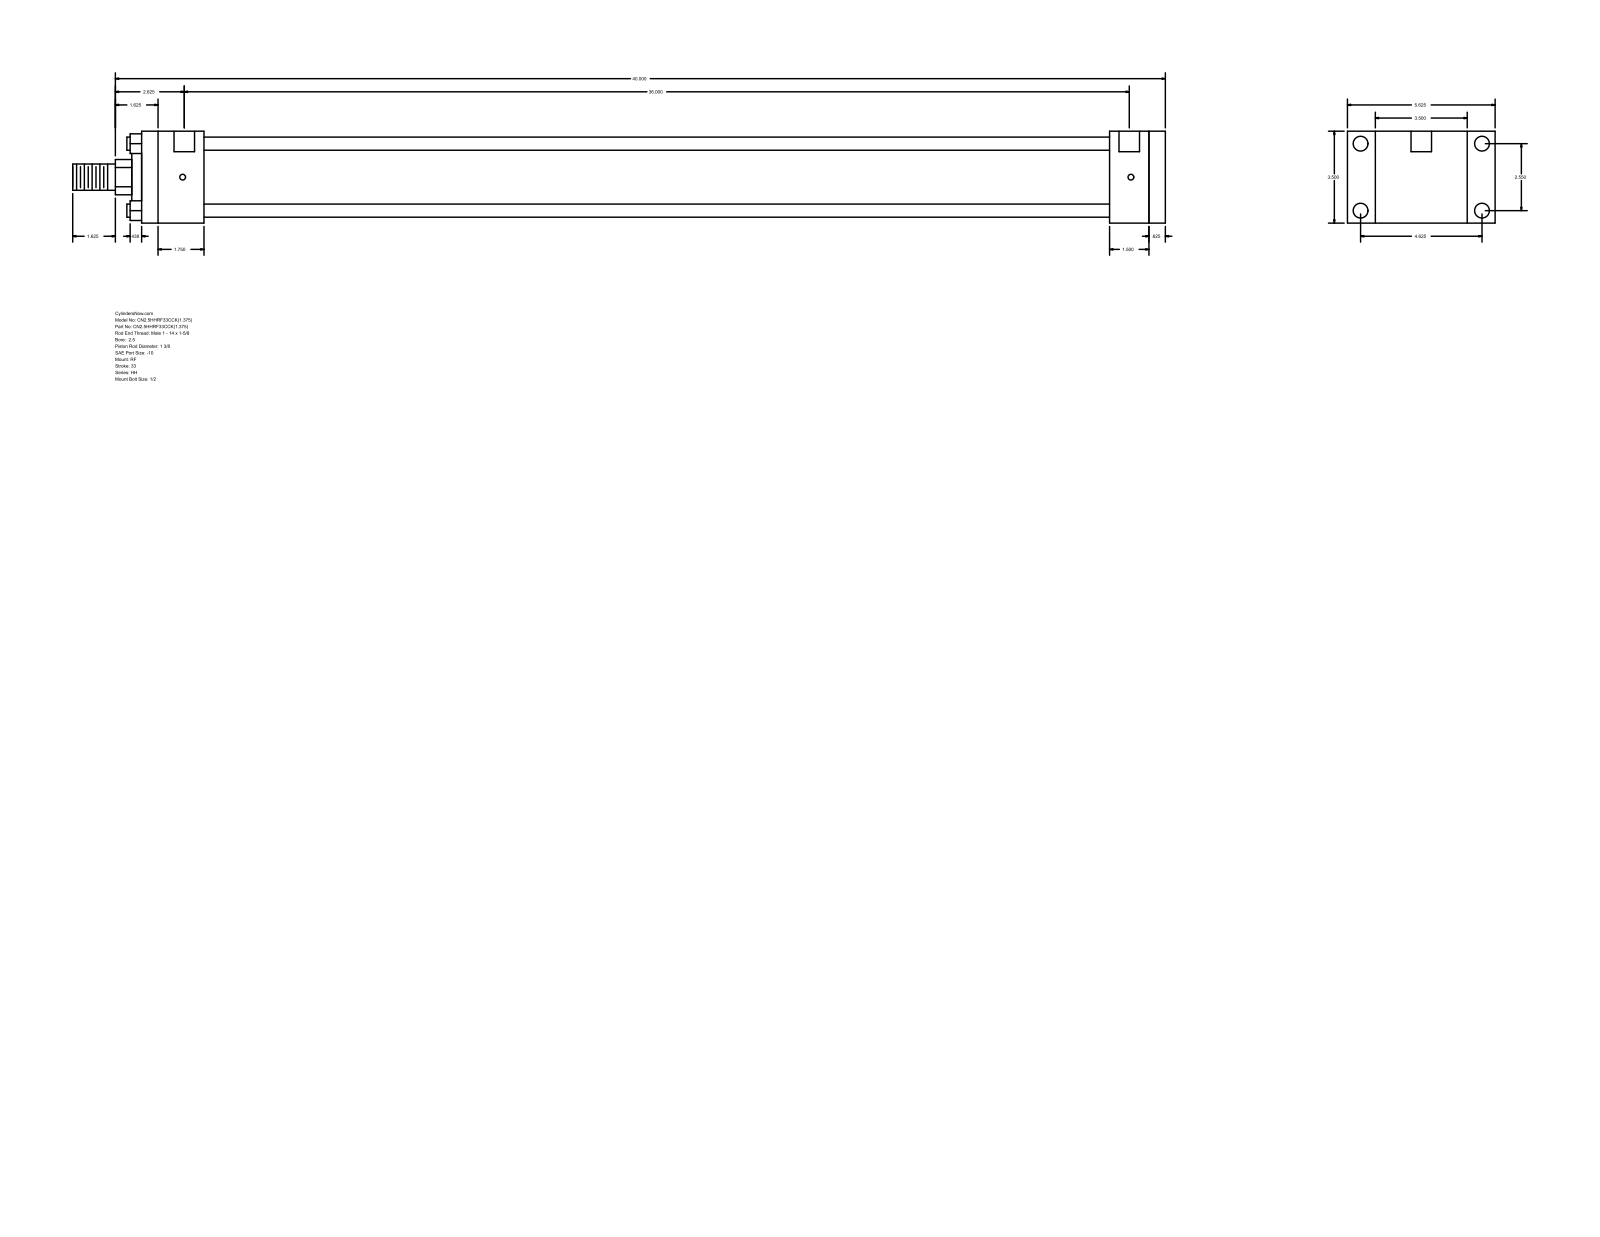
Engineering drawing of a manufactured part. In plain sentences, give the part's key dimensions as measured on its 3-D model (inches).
The part is named "HH_RF__0250_1.375". Its 3-D file was written by "GSSL Pune (CONFIG_CONTROL_DESIGN)". It is 0 solids with 92 faces: 64 planar, 28 cylindrical and 0 other. Overall it measures 41.625 by 5.625 by 3.5 inches. Round holes: 4 of diameter 0.219, 4 of diameter 0.563, 2 of diameter 0.781. Round bosses or shafts: 4 of diameter 0.5, 1 of diameter 2.875, 1 of diameter 2, 1 of diameter 1.375, 1 of diameter 1. Partial cylindrical surfaces (rounded edges, fillets, slot ends): 1 of radius 0.672. The main face-to-face distances are 3.5, 39, 0.625, 38.375, 2.375, 36, 36.625, 36.875, 34.5, 1.5. The hole center spacings are 0.062, 2.55, 4.625, 5.281, 36.063, 36.125, 36.
